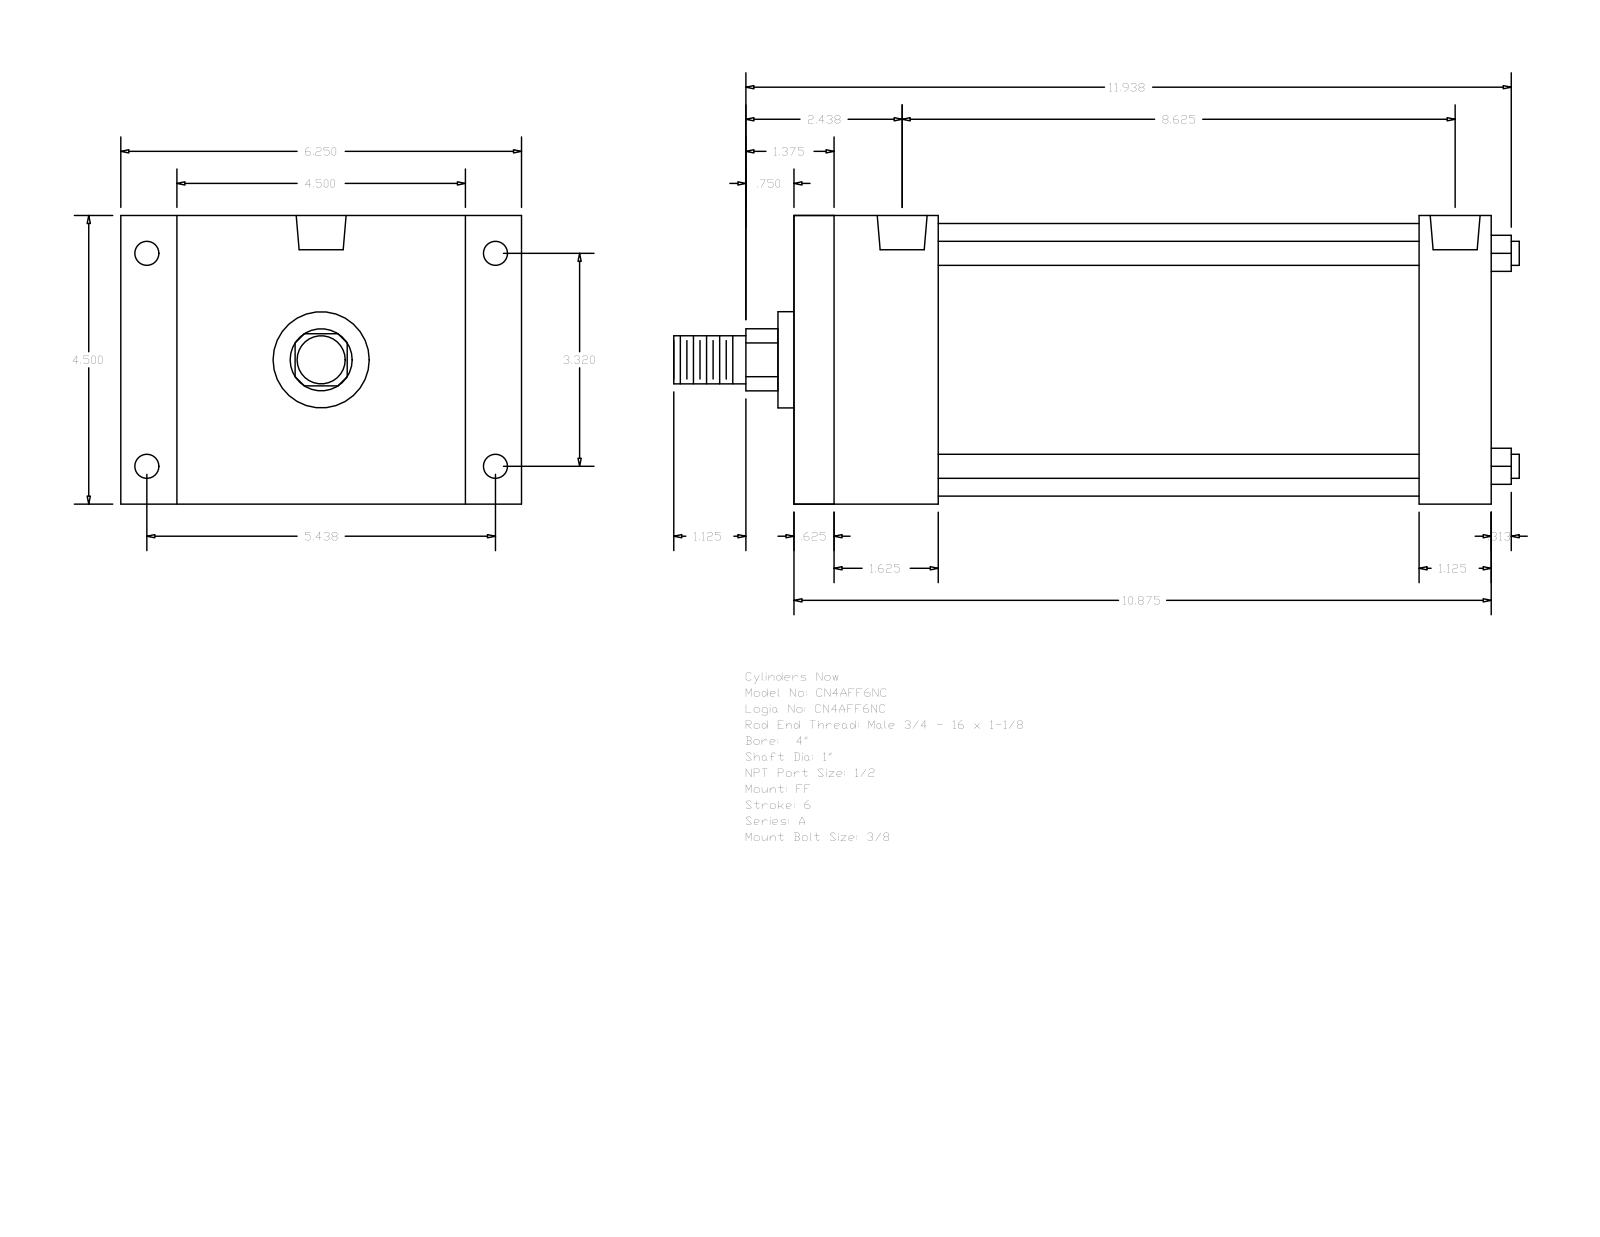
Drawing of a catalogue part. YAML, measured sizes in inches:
part_name: "A_FF__0400_1"
step_written_by: "GSSL Pune (CONFIG_CONTROL_DESIGN)"
units: inches
bodies: {solids: 0, faces: 92, planar: 64, cylindrical: 28, other: 0}
overall_size: [13.187, 6.25, 4.5]
round_holes:
  - {diameter: 0.344, count: 4}
  - {diameter: 0.375, count: 4}
  - {diameter: 0.778, count: 2}
round_bosses_or_shafts:
  - {diameter: 0.375, count: 4}
  - {diameter: 4.25, count: 1}
  - {diameter: 1.5, count: 1}
  - {diameter: 1, count: 1}
  - {diameter: 0.75, count: 1}
partial_cylinders:
  - {radius: 0.484, count: 1}
face_to_face_distances: [4.5, 10.875, 0.625, 10.25, 1.125, 0.875, 5.375, 9.75, 9.125, 2.25]
hole_center_spacings: [0.125, 3.32, 5.438, 6.371, 8.375, 8.5, 8.625]
